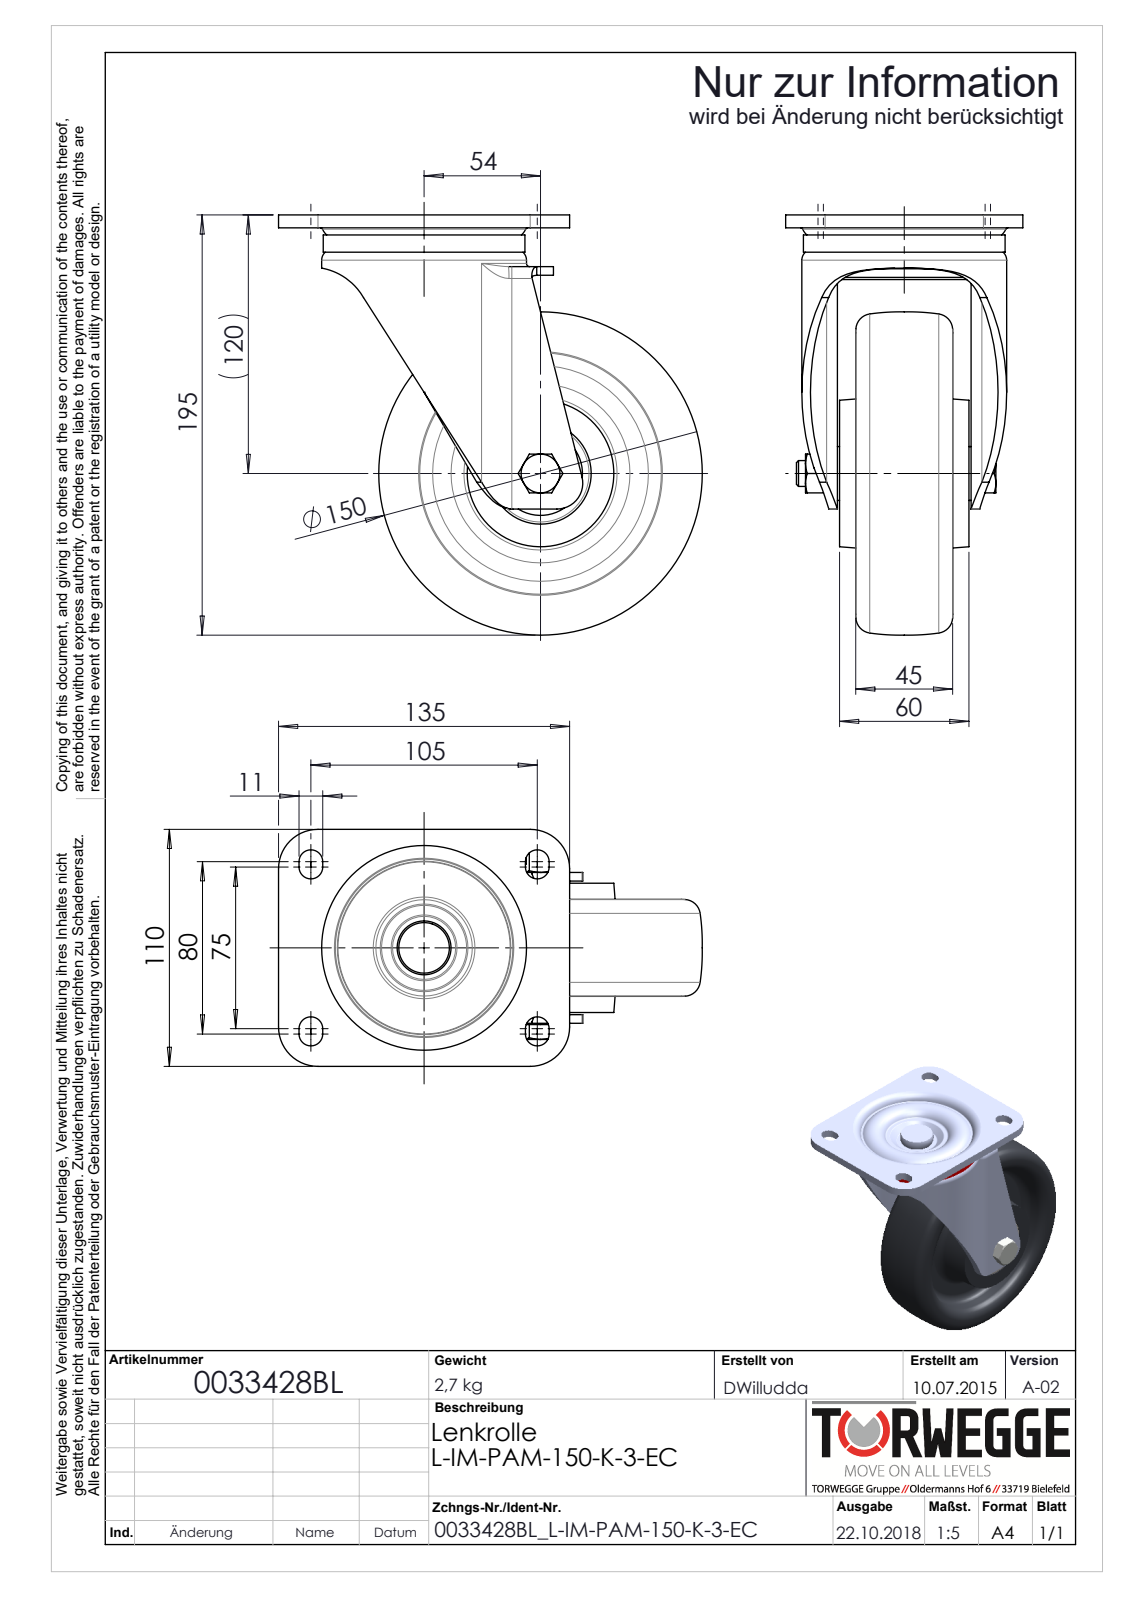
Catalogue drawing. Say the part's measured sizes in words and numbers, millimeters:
The part is named "0033428BL_L-IM-PAM-150-K-3-EC". Its 3-D file was written by "SolidWorks 2016 (AUTOMOTIVE_DESIGN)". It is 15 solids with 720 faces: 324 planar, 184 cylindrical and 212 other. Overall it measures 196.52 by 195.02 by 110 millimeters. Its volume is 829 475 cubic millimeters and its surface area 220 962 square millimeters. Round holes: 1 of diameter 10.2, 1 of diameter 12, 1 of diameter 12.2, 1 of diameter 16.2, 1 of diameter 20, 1 of diameter 20.5, 1 of diameter 35, 1 of diameter 38.9, 1 of diameter 40, 1 of diameter 40.2, 1 of diameter 55.6, 1 of diameter 80.46. Round bosses or shafts: 2 of diameter 18, 1 of diameter 95, 1 of diameter 93.54, 1 of diameter 61.97, 1 of diameter 47, 1 of diameter 28.1, 1 of diameter 25, 1 of diameter 24. Partial cylindrical surfaces (rounded edges, fillets, slot ends): 10 of radius 5.5, 8 of radius 0.31, 7 of radius 0.17, 7 of radius 0.51, 4 of radius 0.1, 4 of radius 0.72, 4 of radius 0.78, 4 of radius 18.29. The main face-to-face distances are 6, 4, 1, 25, 10, 26, 30, 5, 12.5, 35.
